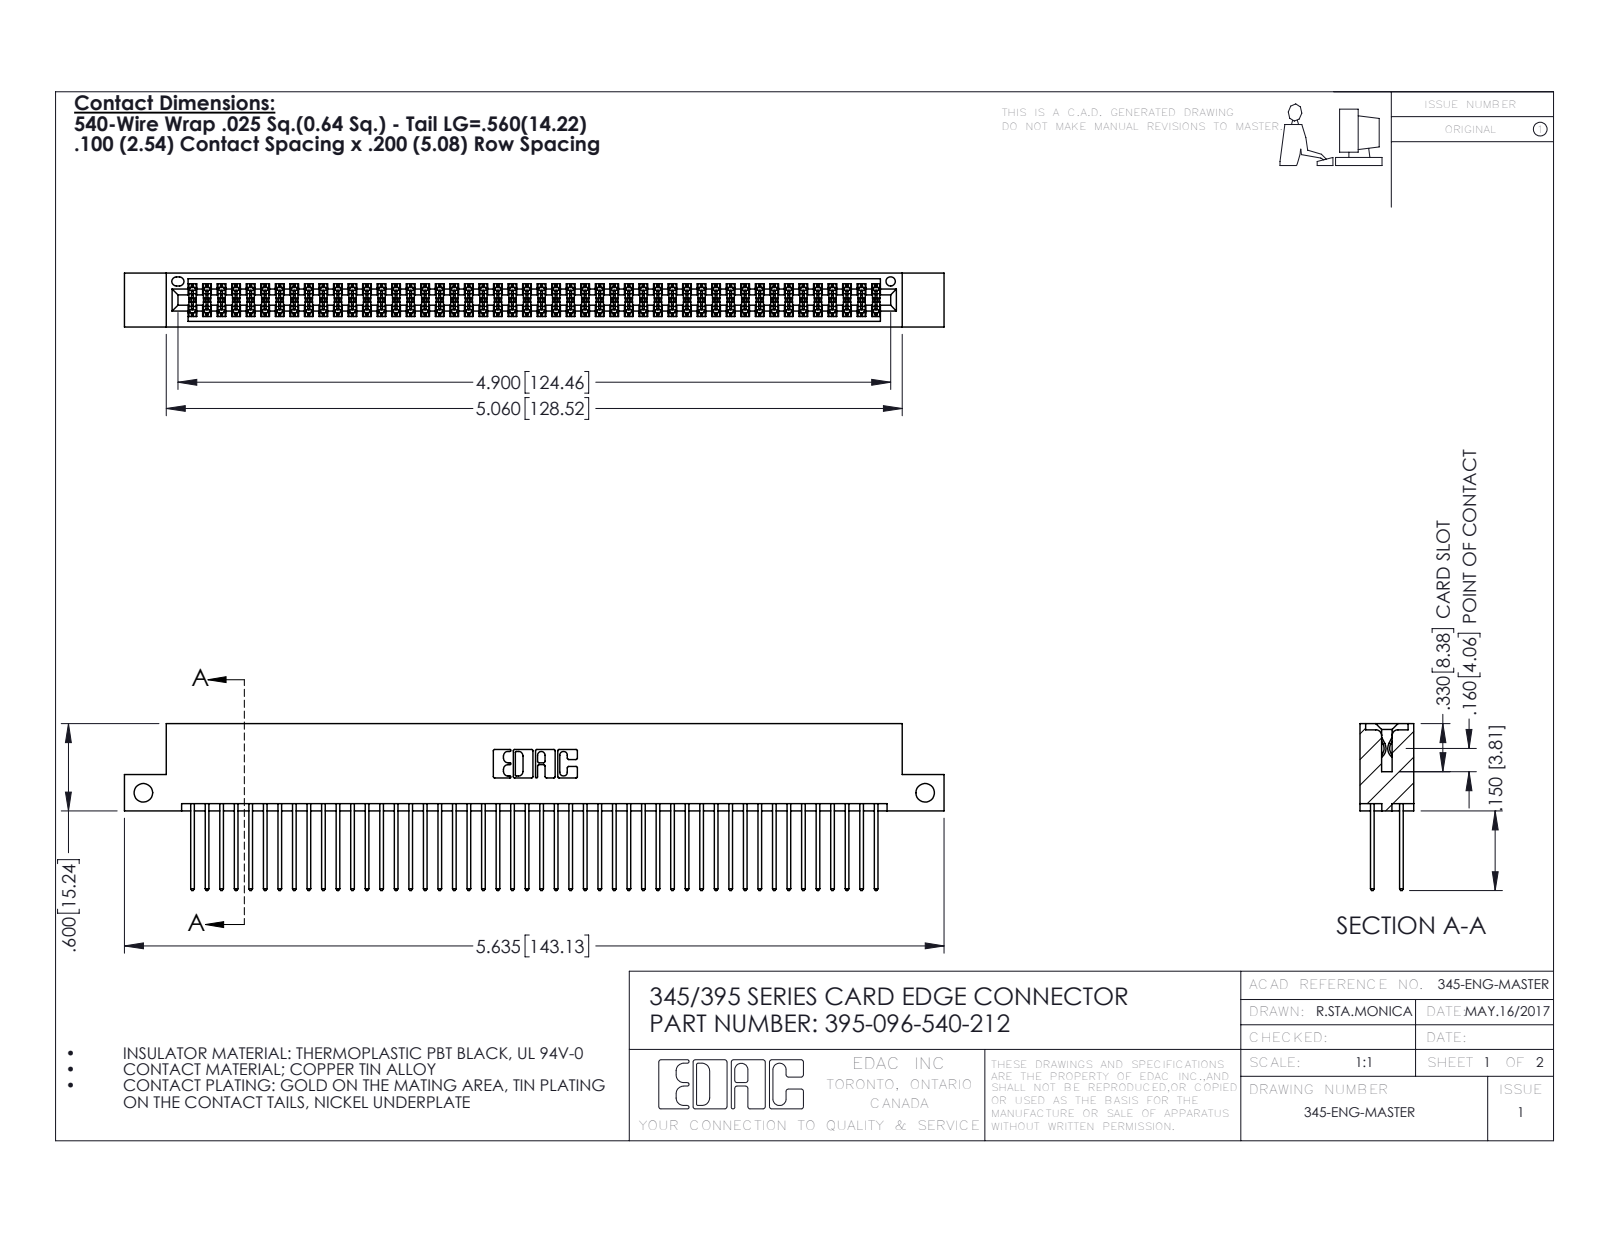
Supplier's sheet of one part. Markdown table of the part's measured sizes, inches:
| quantity | value |
| --- | --- |
| part name | 345 Part_Flush Mounting Lugs - Side Mount; 345-292-001_345-293-140; 395-096-540-212 |
| STEP written by | SolidWorks 2016 (CONFIG_CONTROL_DESIGN) |
| units | inches |
| bodies | 97 solids, 4926 faces (3248 planar, 1678 cylindrical, 0 other) |
| overall size | 5.635 × 1.147 × 0.37 |
| volume | 0.869 in³ |
| surface area | 35.2 in² |
| round holes (diameter × count) | 0.128 × 2, 0.064 × 1 |
| partial cylindrical surfaces (radius × count) | 0.006 × 144, 0.01 × 96, 0.01 × 22, 0.007 × 6, 0.031 × 6, 0.026 × 3, 0.014 × 2, 0.019 × 2 |
| main face-to-face distances | 0.298, 0.072, 0.2, 0.098, 0.272, 0.025, 0.37, 0.225, 0.175, 0.149 |
| hole center spacings | 5.375 |
